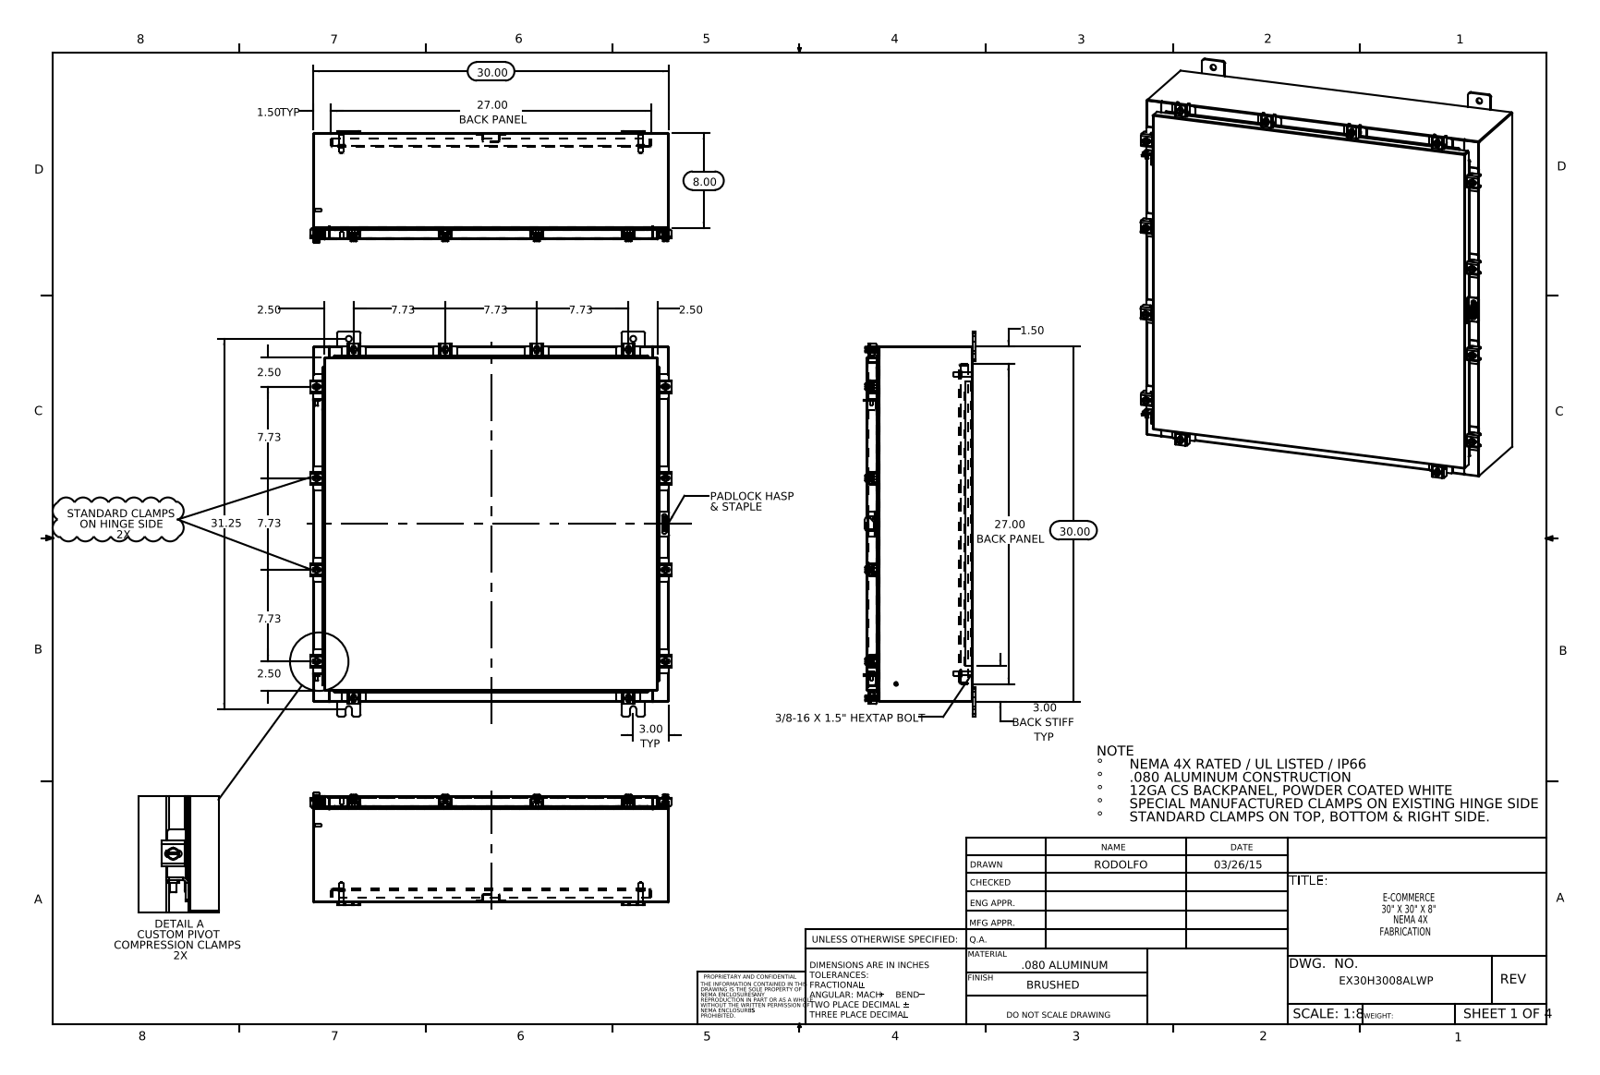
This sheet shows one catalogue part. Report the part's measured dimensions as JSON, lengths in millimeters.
{"part_name": "HW-CLN-NH-20330; EX30H3008ALWP Mounting Studs; N-WMT04X30402202210-00 22104005_DEFAULT; EX30H3008ALWP Top (+8 more)", "step_written_by": "SolidWorks 2014 (CONFIG_CONTROL_DESIGN)", "units": "millimeters", "bodies": {"solids": 92, "faces": 2310, "planar": 1241, "cylindrical": 893, "other": 176}, "overall_size": [825.5, 772.7, 240.1], "volume_mm3": 5324000, "surface_area_mm2": 5201000, "round_holes": [[5.4, 14], [6.6, 14], [12.7, 8], [3.2, 1], [6.4, 1]], "round_bosses_or_shafts": [[12.7, 14], [6.4, 14], [10.1, 12], [15.9, 4], [9.5, 4], [8.4, 4], [8, 2], [6, 2]], "partial_cylinders_radius": [[1.5, 62], [0.3, 30], [3.6, 28], [2.2, 26], [3, 26], [4.8, 24], [2.3, 22], [1.3, 21]], "face_to_face_distances": [1.9, 226.1, 760.1, 224.2, 228, 2.6, 25.4, 27.3, 198.8, 200.7], "hole_center_spacings": [673.3, 927.9, 59.4, 617.5, 695.2, 748.1, 773.4, 112.5]}
